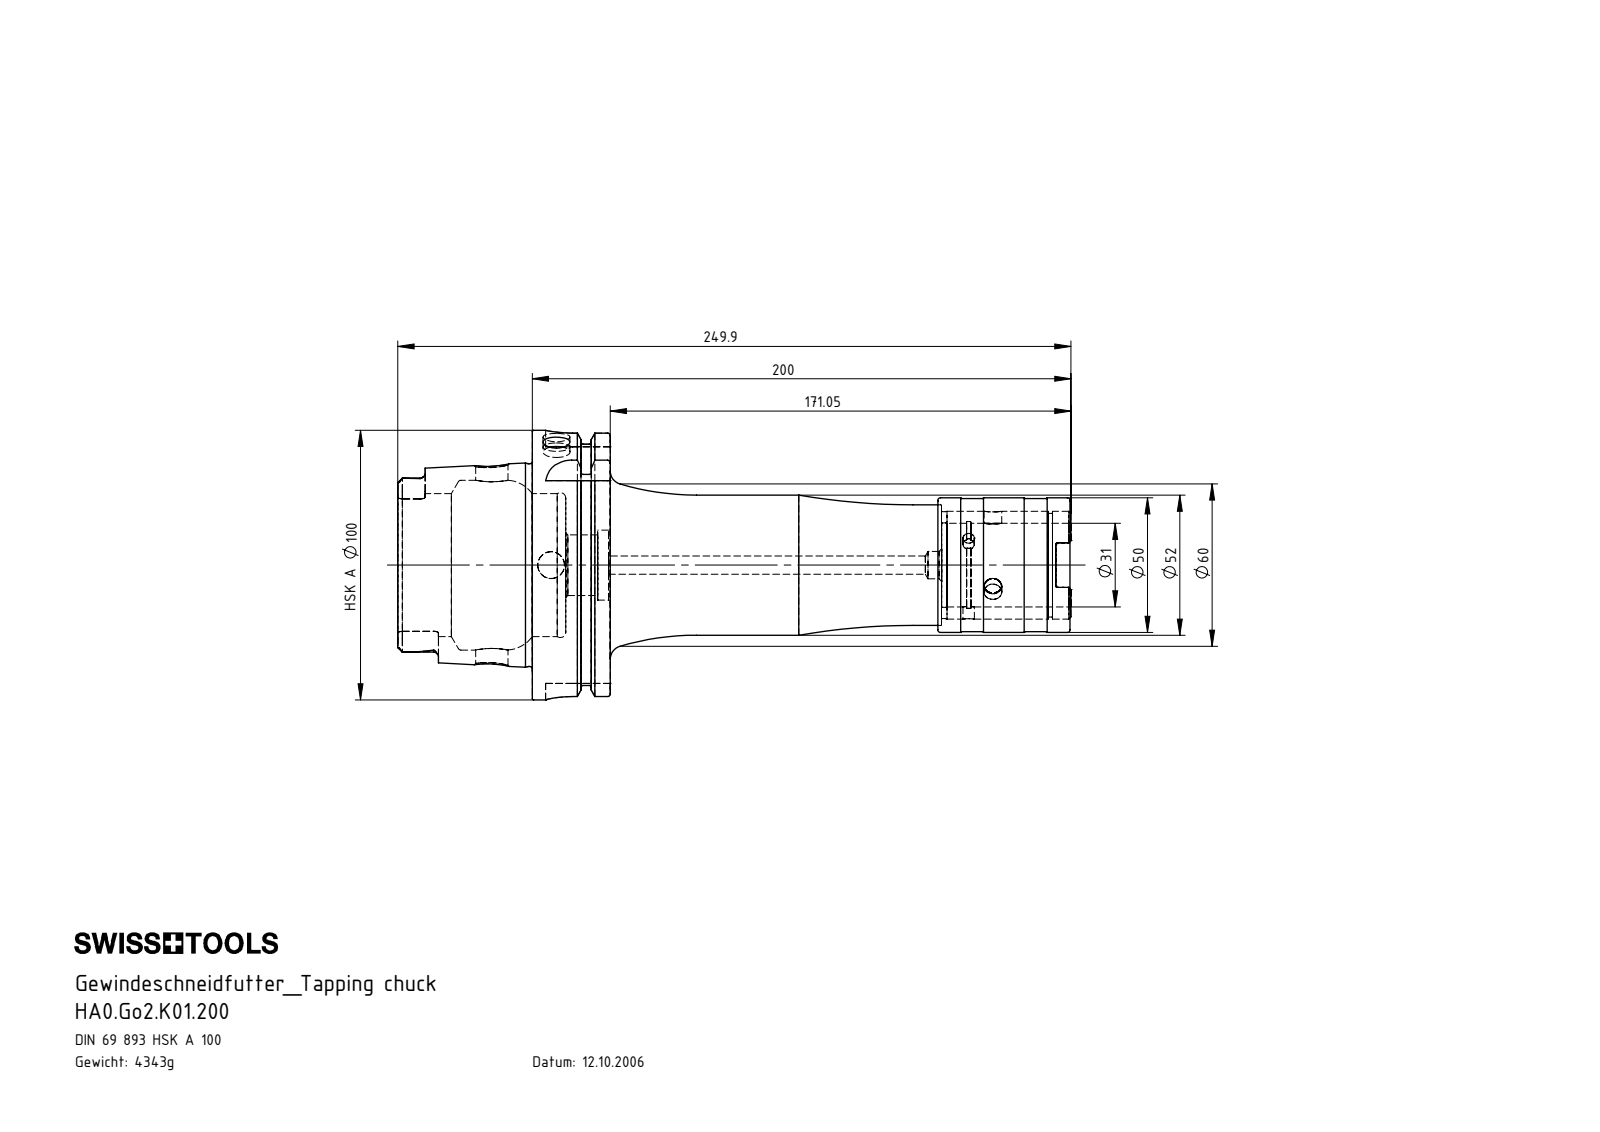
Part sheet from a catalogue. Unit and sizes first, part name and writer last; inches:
Units: inches
Overall size (bounding box): 9.839 × 3.937 × 3.937
Round holes (diameter × count): ⌀0.165 ×3, ⌀0.26 ×3, ⌀0.394 ×3, ⌀0.098 ×1, ⌀0.268 ×1, ⌀0.398 ×1, ⌀0.472 ×1, ⌀0.886 ×1, ⌀1.024 ×1, ⌀1.22 ×1, ⌀1.232 ×1, ⌀1.274 ×1
Round bosses / shafts (diameter × count): ⌀3.937 ×1, ⌀3.62 ×1, ⌀2.963 ×1, ⌀2.047 ×1, ⌀1.969 ×1, ⌀1.945 ×1, ⌀1.762 ×1, ⌀1.575 ×1
Partial cylindrical surfaces — rounded edges, fillets, slot ends (radius × count): R0.075 ×6, R0.192 ×4, R0.394 ×4, R0.122 ×3, R0.02 ×2
Main face-to-face distances: 1.14, 0.49, 0.65, 0.026, 4.87, 1.965, 2.455, 3.104, 8.447, 6.482
Hole centre spacings: 0.354, 6.969, 7.323
Volume: 33.75 in³ · Surface area: 162.4 in²
Bodies: 10 solids, 377 faces (83 planar, 122 cylindrical, 172 other)
Part name (STEP PRODUCT): Feder gross Go2_vorgespannt; HA0-Go2.K01.200_C_Fertigbearbeitung; Feder klein Go2_gespannt; Kugel Go2 (+6 more)
STEP written by: SolidWorks 2017 (CONFIG_CONTROL_DESIGN)
